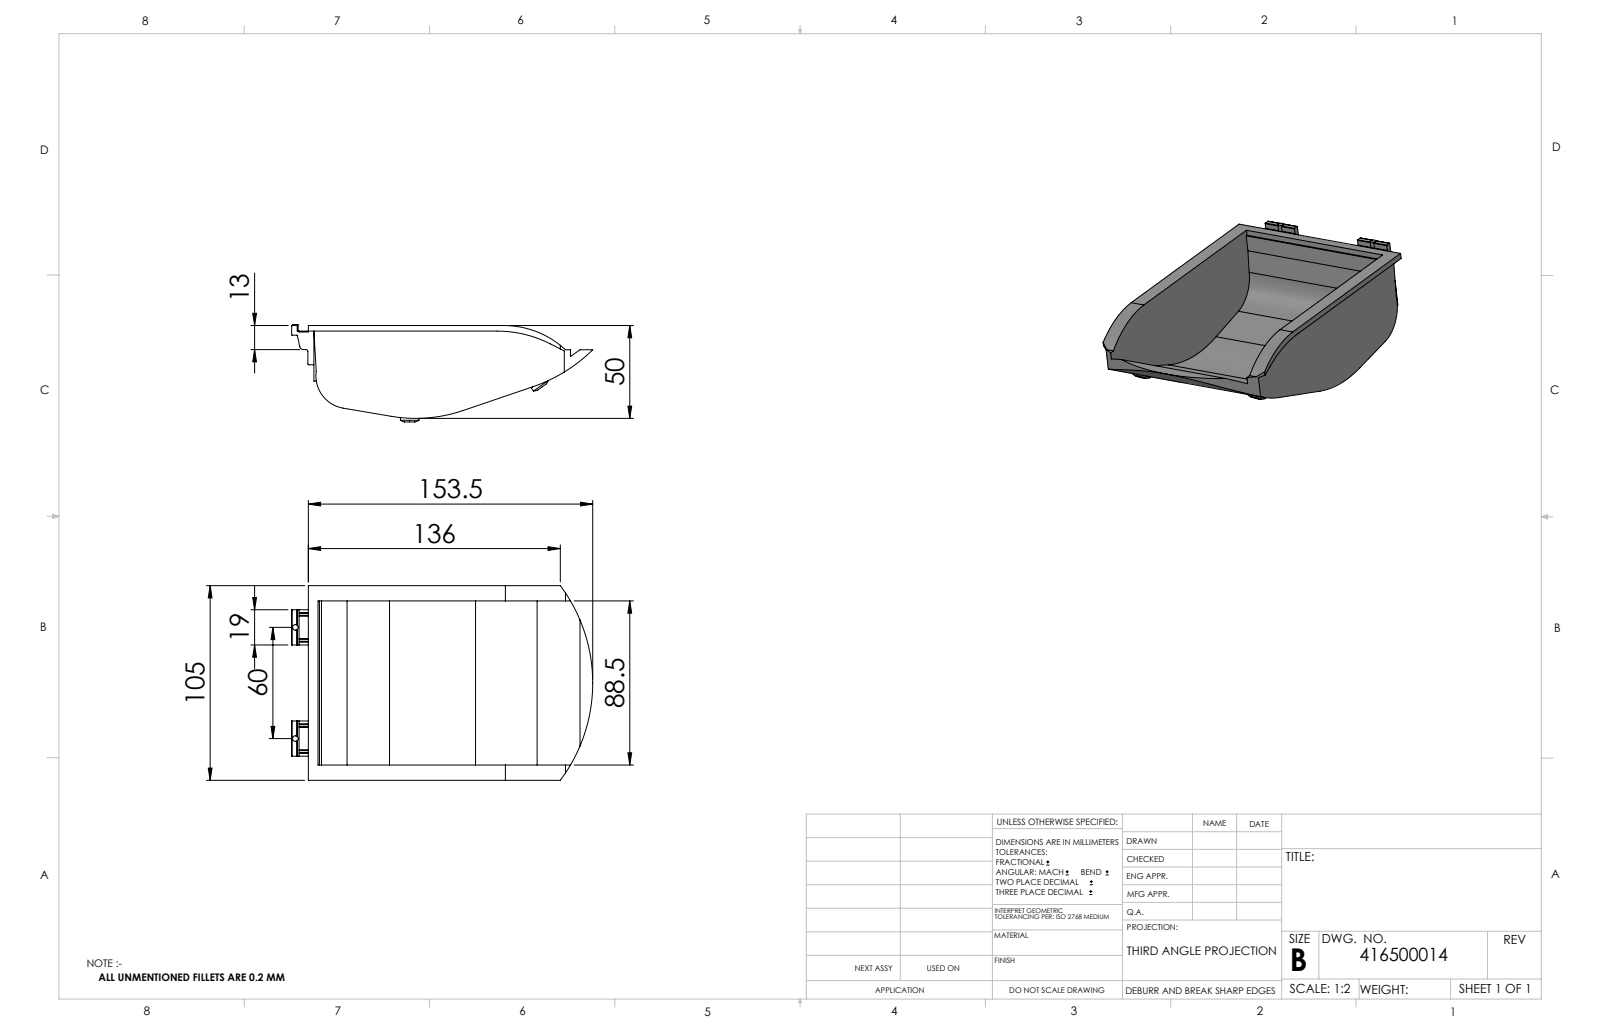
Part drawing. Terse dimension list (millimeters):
name: 416500014_c_1
written by: SolidWorks 2014 (CONFIG_CONTROL_DESIGN)
unit: mm
bodies: 1 solid, 159 faces (103 planar, 48 cylindrical, 8 other)
size: 162.5 × 105 × 52.5
volume: 110 403 mm³; area: 63 346 mm²
bosses: 4× ⌀10, 2× ⌀3
rounds: 6× R0.5, 3× R0.2, 2× R17.65, 2× R79, 1× R1, 1× R2, 1× R49.07, 1× R63.24
face distances: 5.23, 93.77, 99, 88.54, 3, 8.23, 96.77, 102, 6, 14.5
